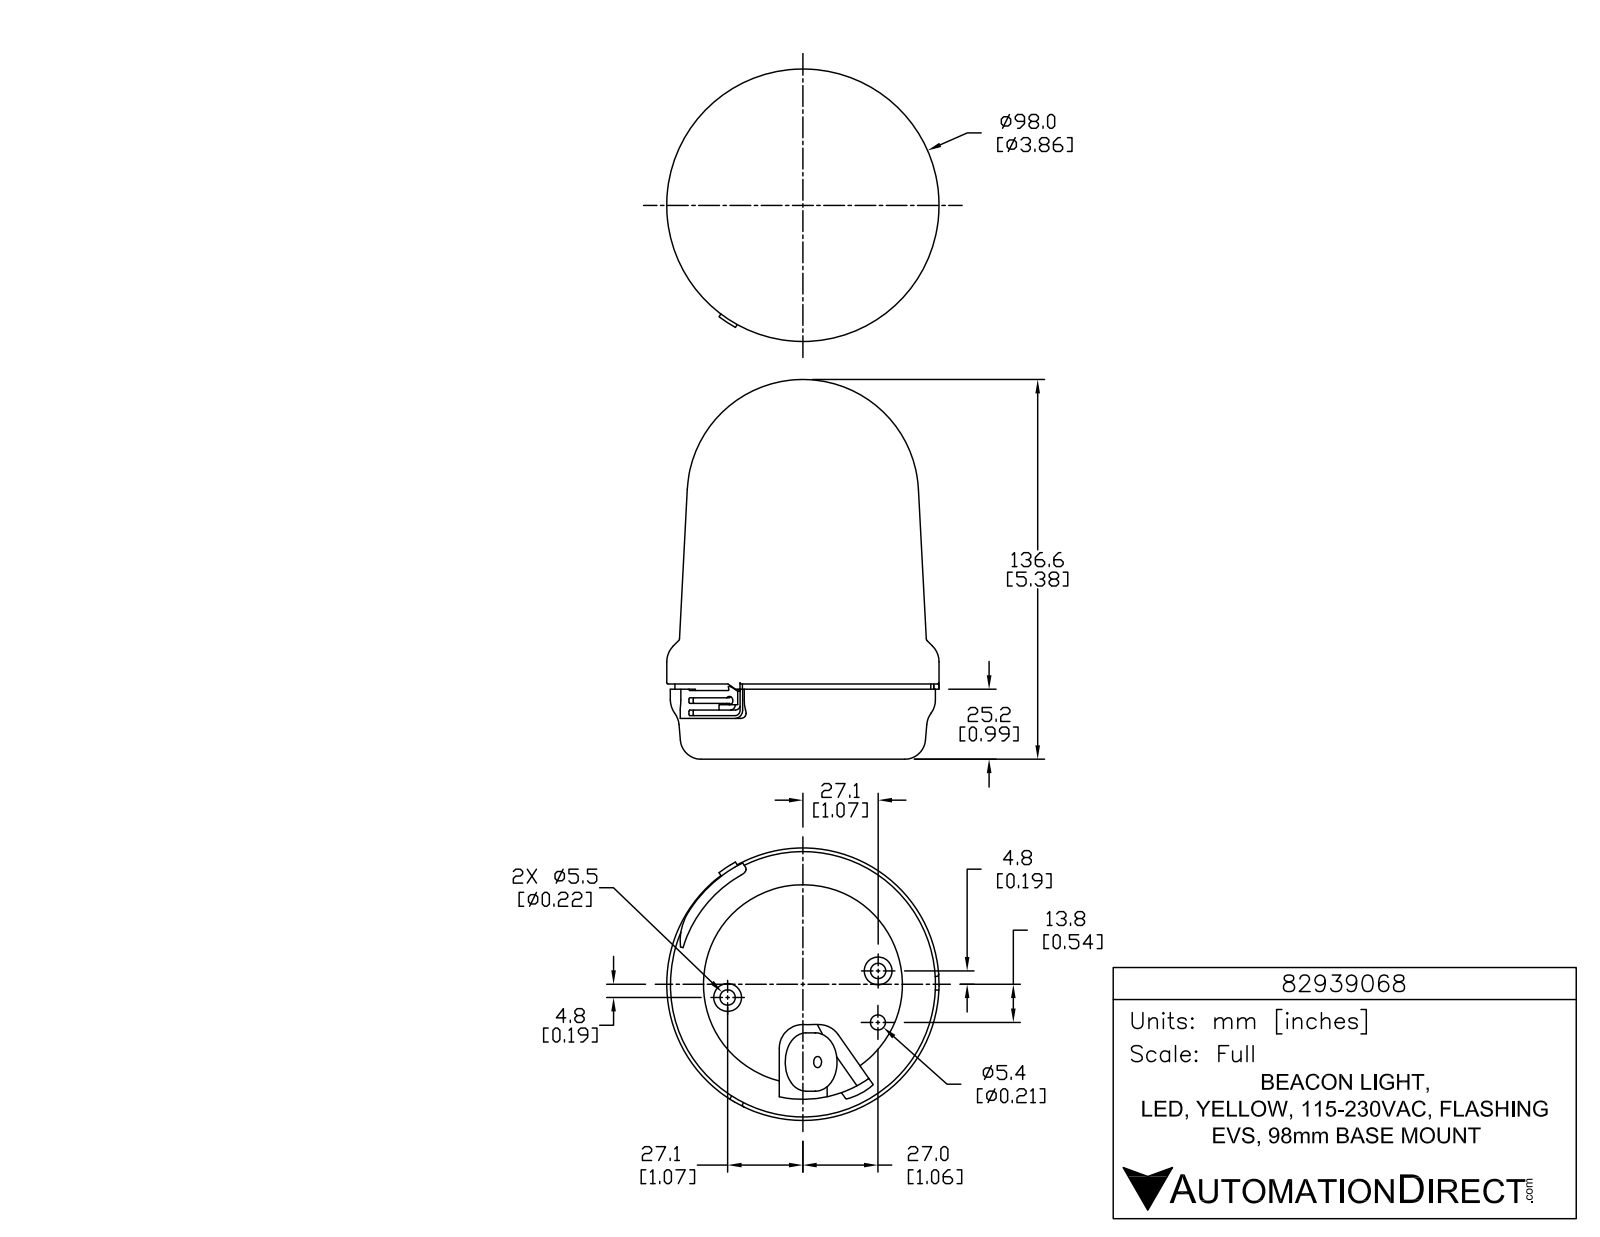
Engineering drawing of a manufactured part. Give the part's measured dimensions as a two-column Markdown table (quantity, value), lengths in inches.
| quantity | value |
| --- | --- |
| part name | 82939068 |
| STEP written by | SolidWorks 2017 (AUTOMOTIVE_DESIGN) |
| units | inches |
| bodies | 1 solid, 872 faces (566 planar, 204 cylindrical, 102 other) |
| overall size | 5.378 × 3.858 × 3.858 |
| volume | 44.69 in³ |
| surface area | 73.66 in² |
| round holes (diameter × count) | 0.059 × 3, 0.217 × 2, 0.157 × 1, 0.213 × 1, 2.819 × 1 |
| round bosses / shafts (diameter × count) | 0.339 × 3, 0.084 × 3, 0.394 × 2, 3.858 × 1, 3.756 × 1, 3.626 × 1, 0.827 × 1 |
| partial cylindrical surfaces (radius × count) | 0.005 × 9, 0.005 × 6, 0.012 × 6, 0.012 × 6, 0.012 × 6, 0.196 × 6, 0.02 × 5, 0.039 × 4 |
| main face-to-face distances | 1.045, 0.972, 0.073, 0.02, 0.992, 1.065, 0.236, 0.579, 0.559, 0.413 |
| hole center spacings | 1.083, 0.73, 1.193, 2.158, 2.165 |
